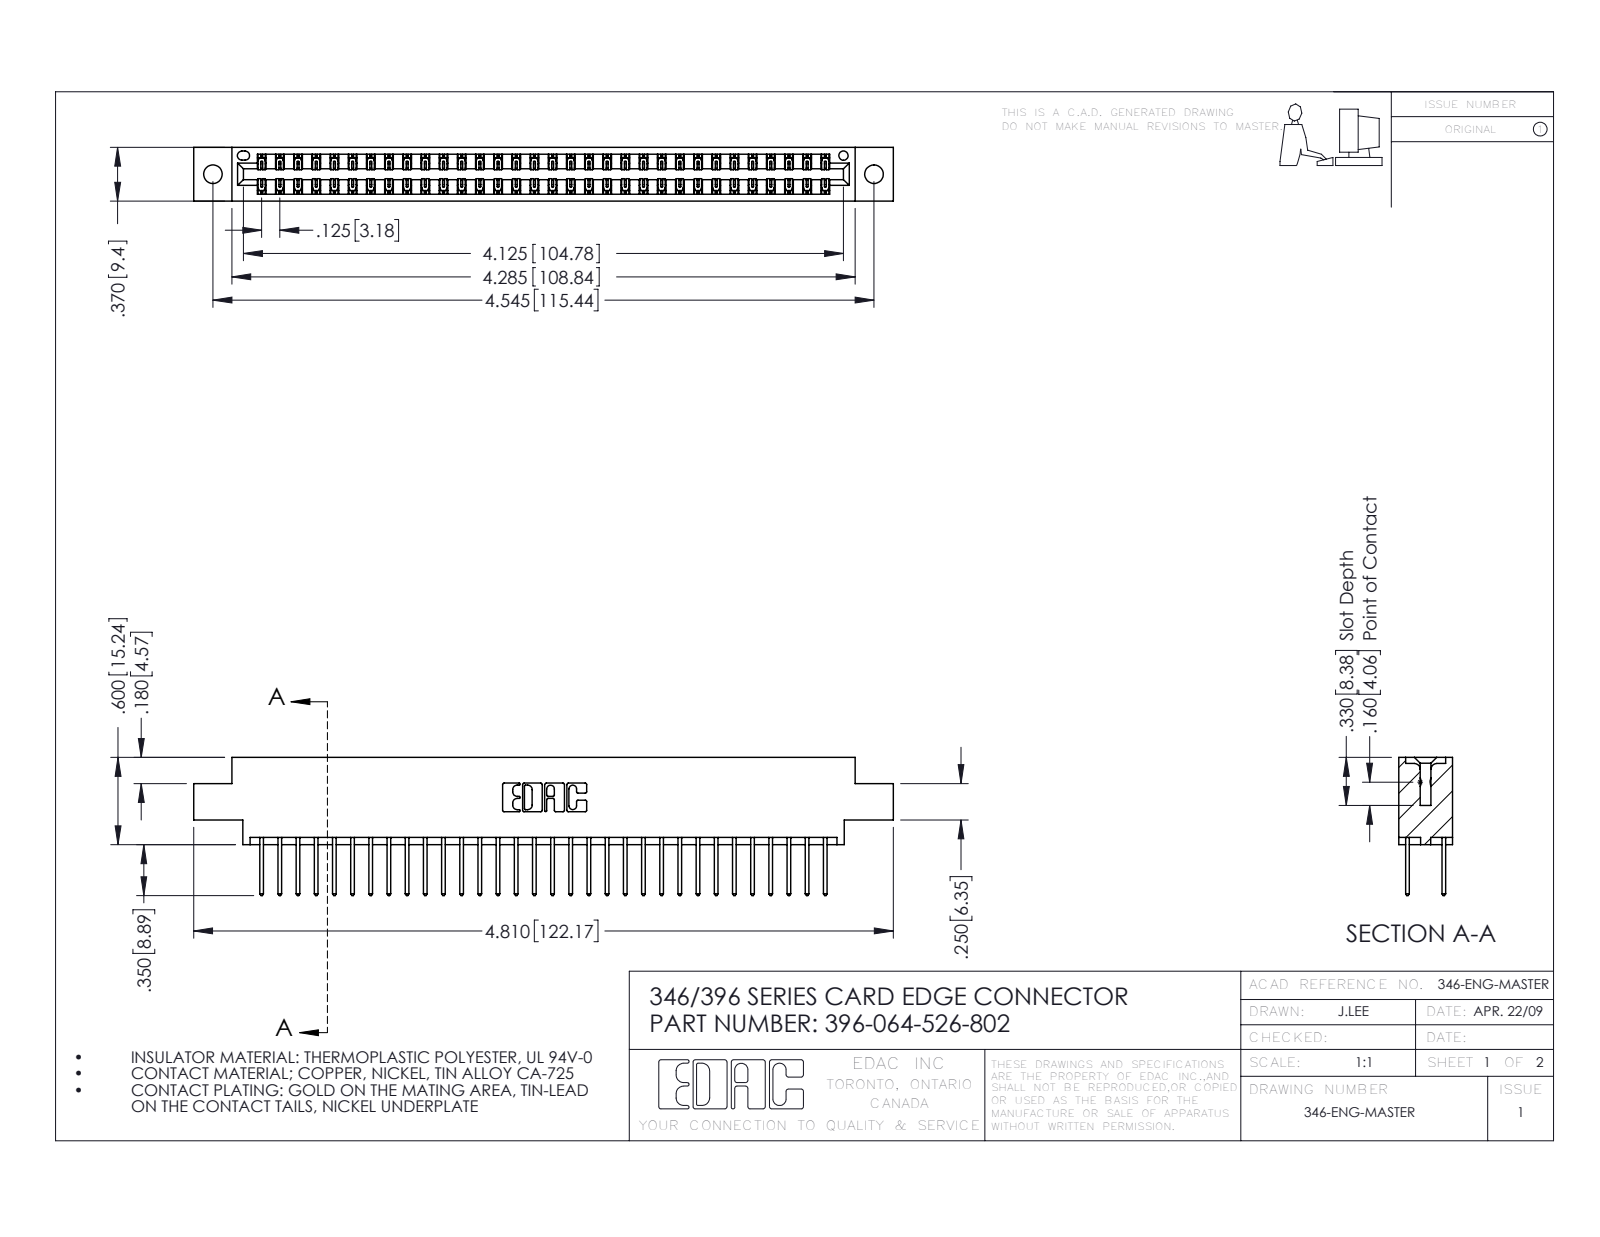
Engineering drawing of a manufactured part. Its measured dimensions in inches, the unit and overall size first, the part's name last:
Units: inches
Overall size (bounding box): 4.81 × 0.95 × 0.37
Round holes (diameter × count): ⌀0.128 ×2, ⌀0.064 ×1
Partial cylindrical surfaces — rounded edges, fillets, slot ends (radius × count): R0.006 ×96, R0.01 ×64, R0.01 ×22, R0.007 ×6, R0.031 ×6, R0.026 ×3, R0.014 ×2, R0.022 ×2
Main face-to-face distances: 0.048, 0.322, 0.25, 0.37, 0.072, 0.298, 0.025, 0.275, 0.148, 0.222
Hole centre spacings: 0.246, 4.337, 4.545
Volume: 0.717 in³ · Surface area: 25.38 in²
Bodies: 65 solids, 3454 faces (2320 planar, 1134 cylindrical, 0 other)
Part name (STEP PRODUCT): 345-292-001_345-293-126; 396-064-526-802; 346 Part_0.170 Offset - 0.128 Dia
STEP written by: SolidWorks 2016 (CONFIG_CONTROL_DESIGN)
